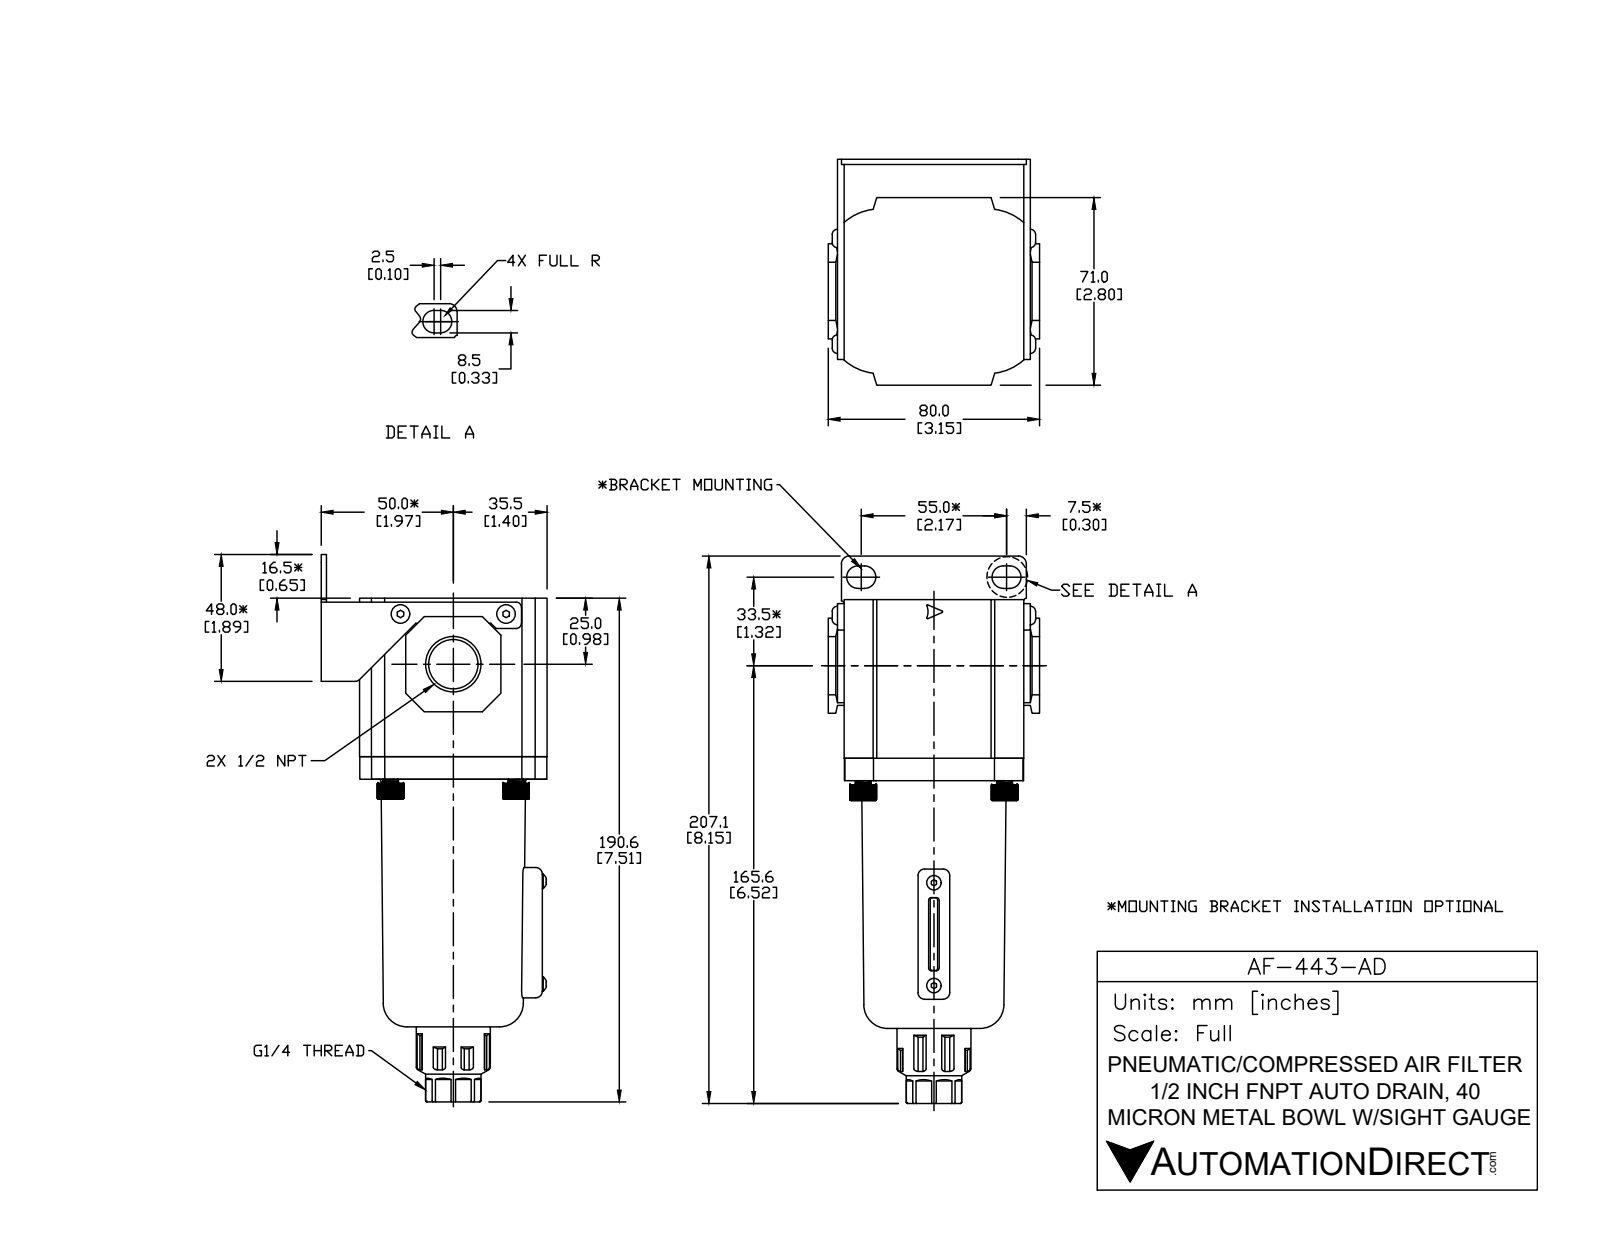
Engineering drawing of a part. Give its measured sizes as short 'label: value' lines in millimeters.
name: AF-443-AD
written by: SolidWorks 2015 (CONFIG_CONTROL_DESIGN)
unit: mm
bodies: 9 solids, 416 faces (245 planar, 98 cylindrical, 73 other)
size: 207.13 × 85.7 × 80
volume: 549 369 mm³; area: 76 746 mm²
holes: 2× ⌀3.4, 1× ⌀6.2, 1× ⌀17.86
bosses: 4× ⌀10, 2× ⌀5.5, 1× ⌀28, 1× ⌀21
rounds: 8× R1.3, 8× R2.5, 8× R9.5, 6× R0.5, 5× R2, 4× R0.3, 4× R1, 4× R4.25
face distances: 2.5, 60, 68, 14.5, 12, 70.5, 71, 85.5, 83, 8.5
hole spacings: 27.59, 40
